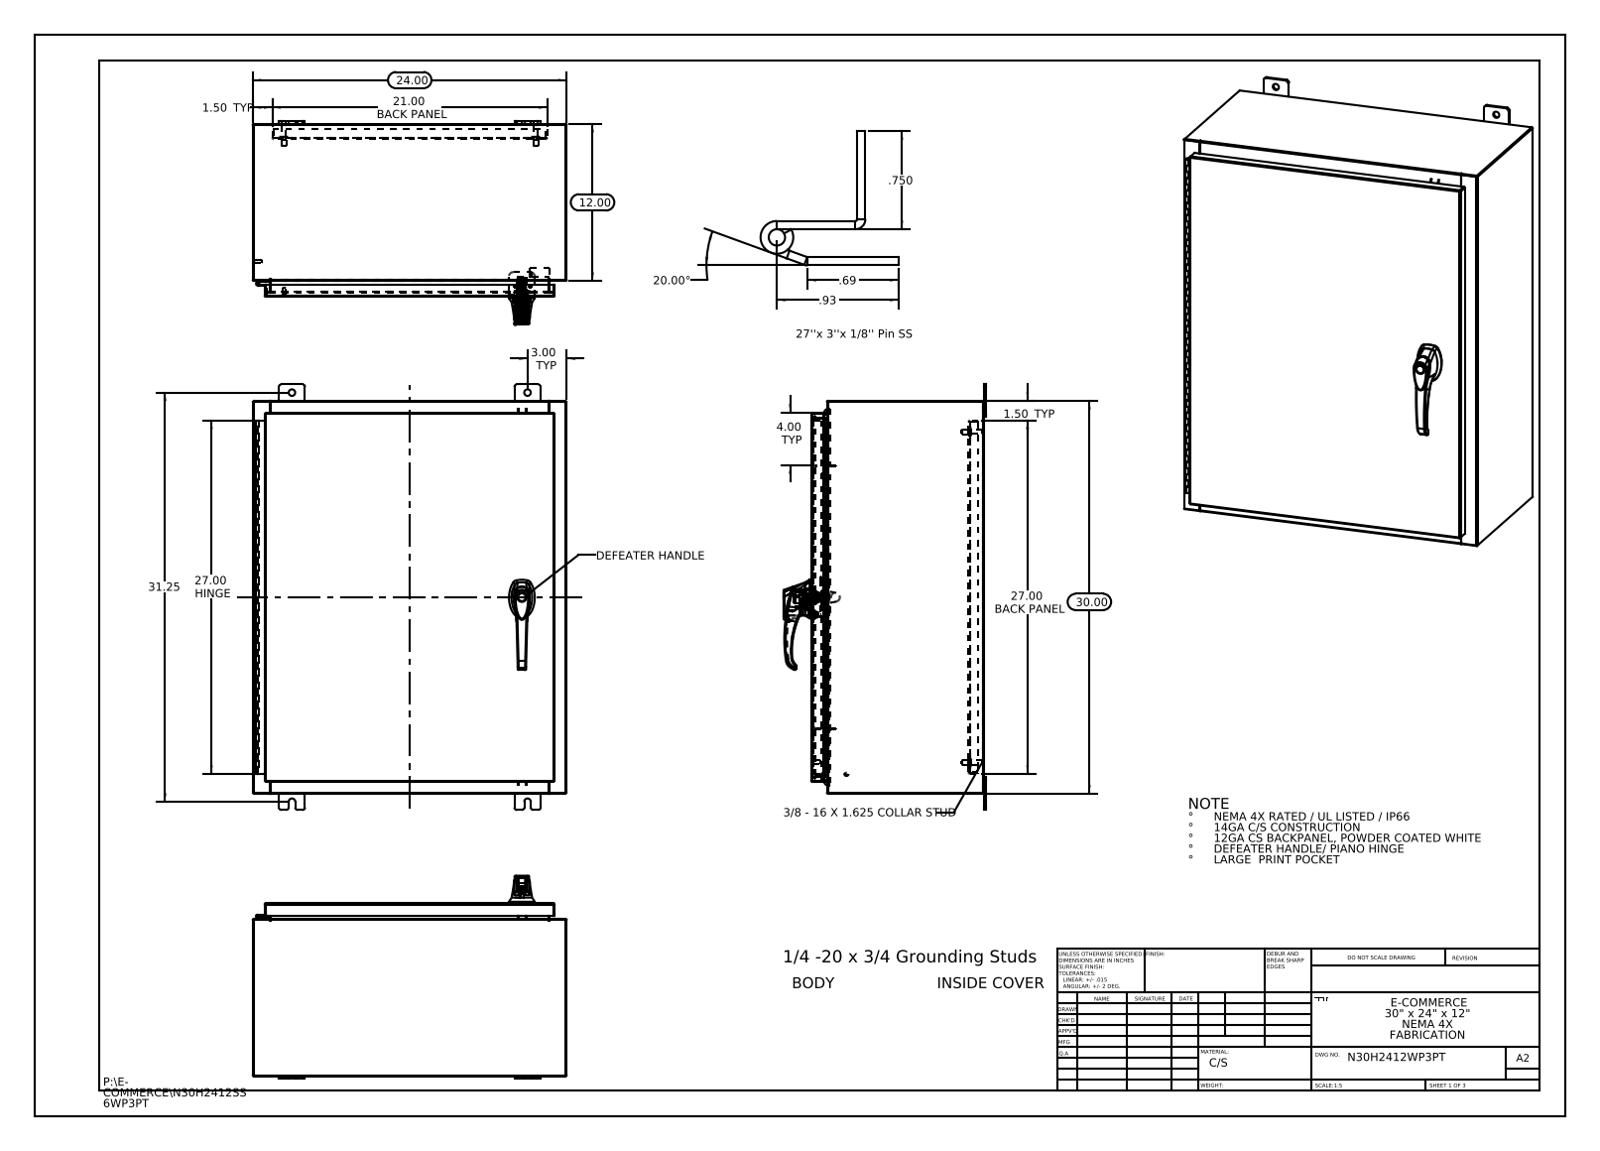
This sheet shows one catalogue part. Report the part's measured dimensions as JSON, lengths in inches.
{"part_name": "N30H2412SS6WP3PT Defeater Handle Rod; N30H2412SS6WP3PT Top; 297025; N30H2412SS6WP3PT Mounting Studs (+8 more)", "step_written_by": "SolidWorks 2013 (CONFIG_CONTROL_DESIGN)", "units": "inches", "bodies": {"solids": 37, "faces": 2662, "planar": 971, "cylindrical": 993, "other": 698}, "overall_size": [32.5, 24, 15.495], "volume_in3": 304.2, "surface_area_in2": 7576, "round_holes": [[0.5, 8], [0.25, 4], [0.138, 3], [0.161, 3], [0.079, 2], [0.203, 2], [0.313, 2], [0.437, 2], [0.125, 1], [0.125, 1], [0.197, 1], [0.276, 1]], "round_bosses_or_shafts": [[0.625, 4], [0.375, 4], [0.33, 4], [0.157, 4], [0.14, 4], [0.315, 3], [0.236, 3], [1.181, 1]], "partial_cylinders_radius": [[0.118, 37], [0.006, 33], [0.013, 24], [0.19, 24], [0.088, 18], [0.039, 15], [0.028, 12], [0.008, 6]], "face_to_face_distances": [0.075, 13.126, 23.925, 0.104, 13.051, 13.201, 1, 29.925, 1.075, 12.051], "hole_center_spacings": [8.369, 0.295, 0.625, 0.841, 1.25, 1.313, 1.561, 1.858]}
